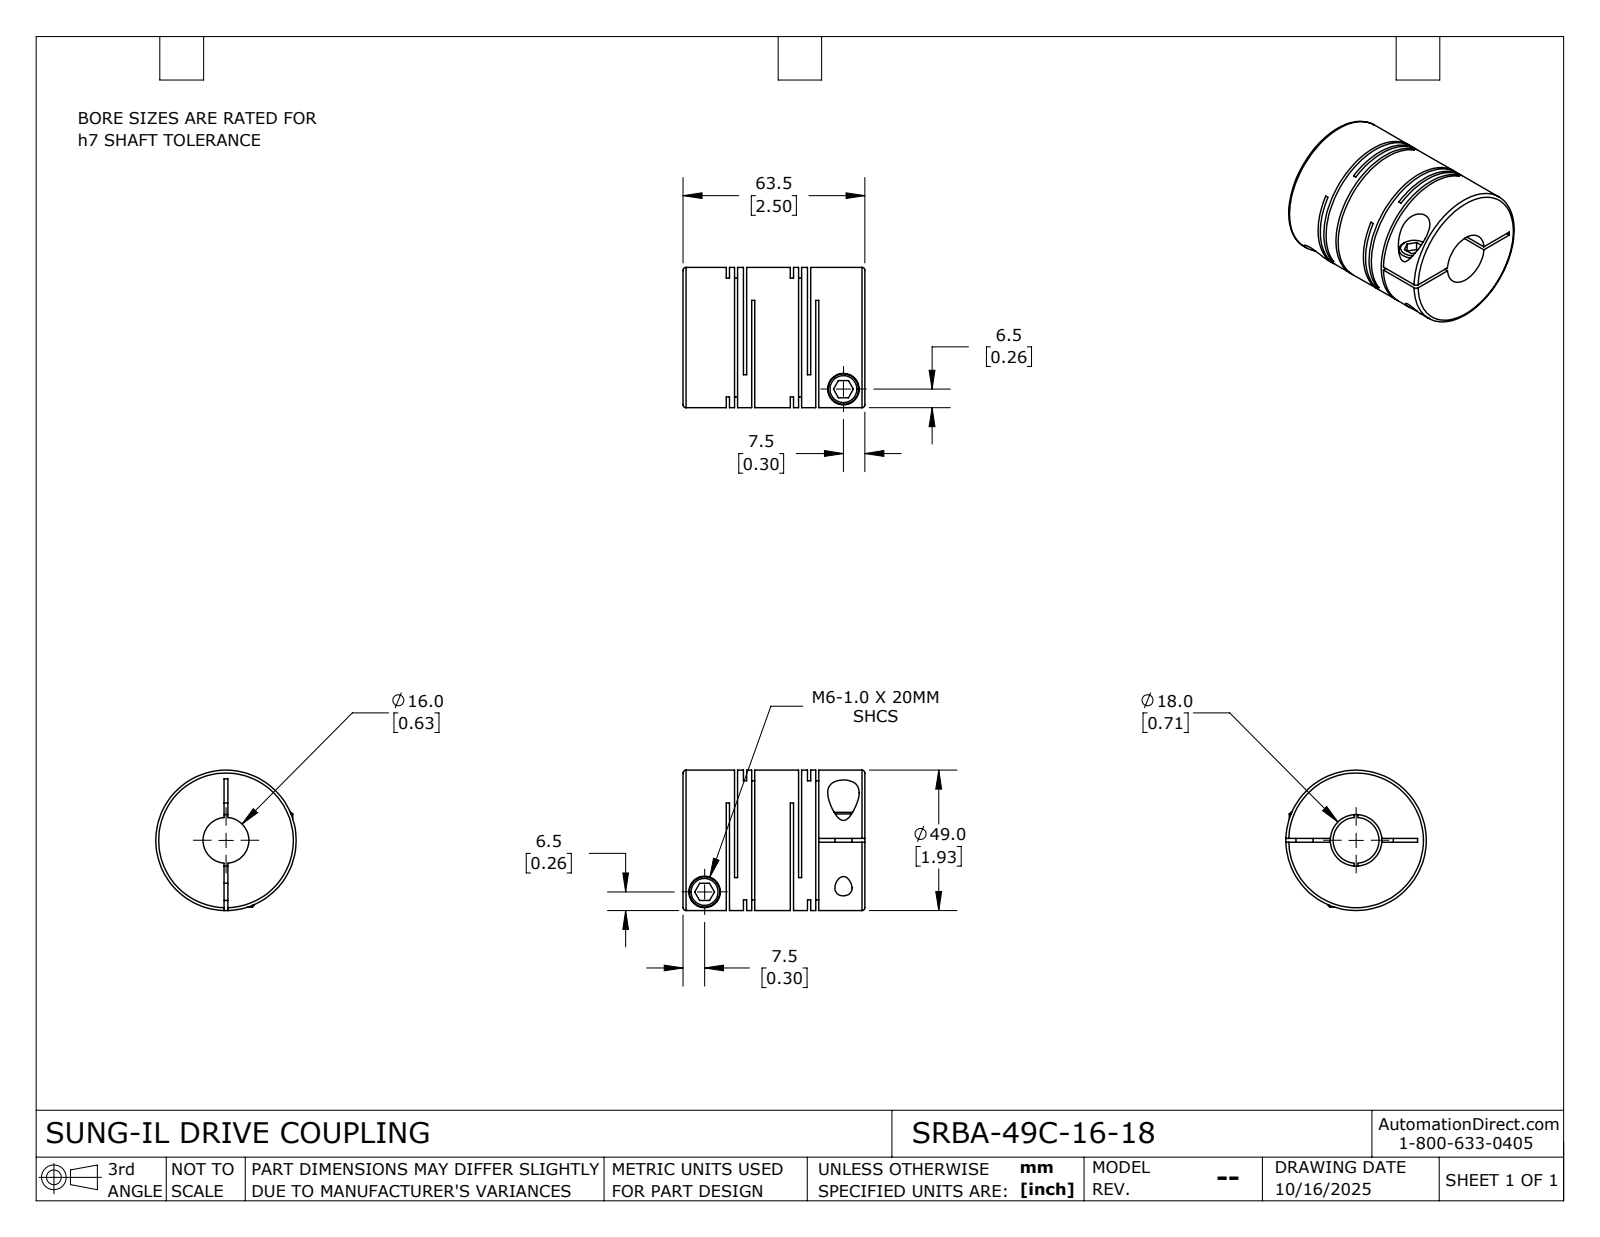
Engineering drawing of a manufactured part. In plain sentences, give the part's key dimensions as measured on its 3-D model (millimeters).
The part is named "SRBA-49C-16-18". Its 3-D file was written by "SolidWorks 2024 (CONFIG_CONTROL_DESIGN)". It is 1 solid with 115 faces: 60 planar, 42 cylindrical and 13 other. Overall it measures 63.5 by 49 by 49 millimeters. Its volume is 90 160 cubic millimeters and its surface area 38 888 square millimeters. Round holes: 2 of diameter 6, 2 of diameter 11, 1 of diameter 16, 1 of diameter 18. Round bosses or shafts: 2 of diameter 10.6, 1 of diameter 49. The main face-to-face distances are 6, 1.1, 22.35, 2.85, 21.25, 3.15, 19.5, 16.35, 1.75, 4.9.
